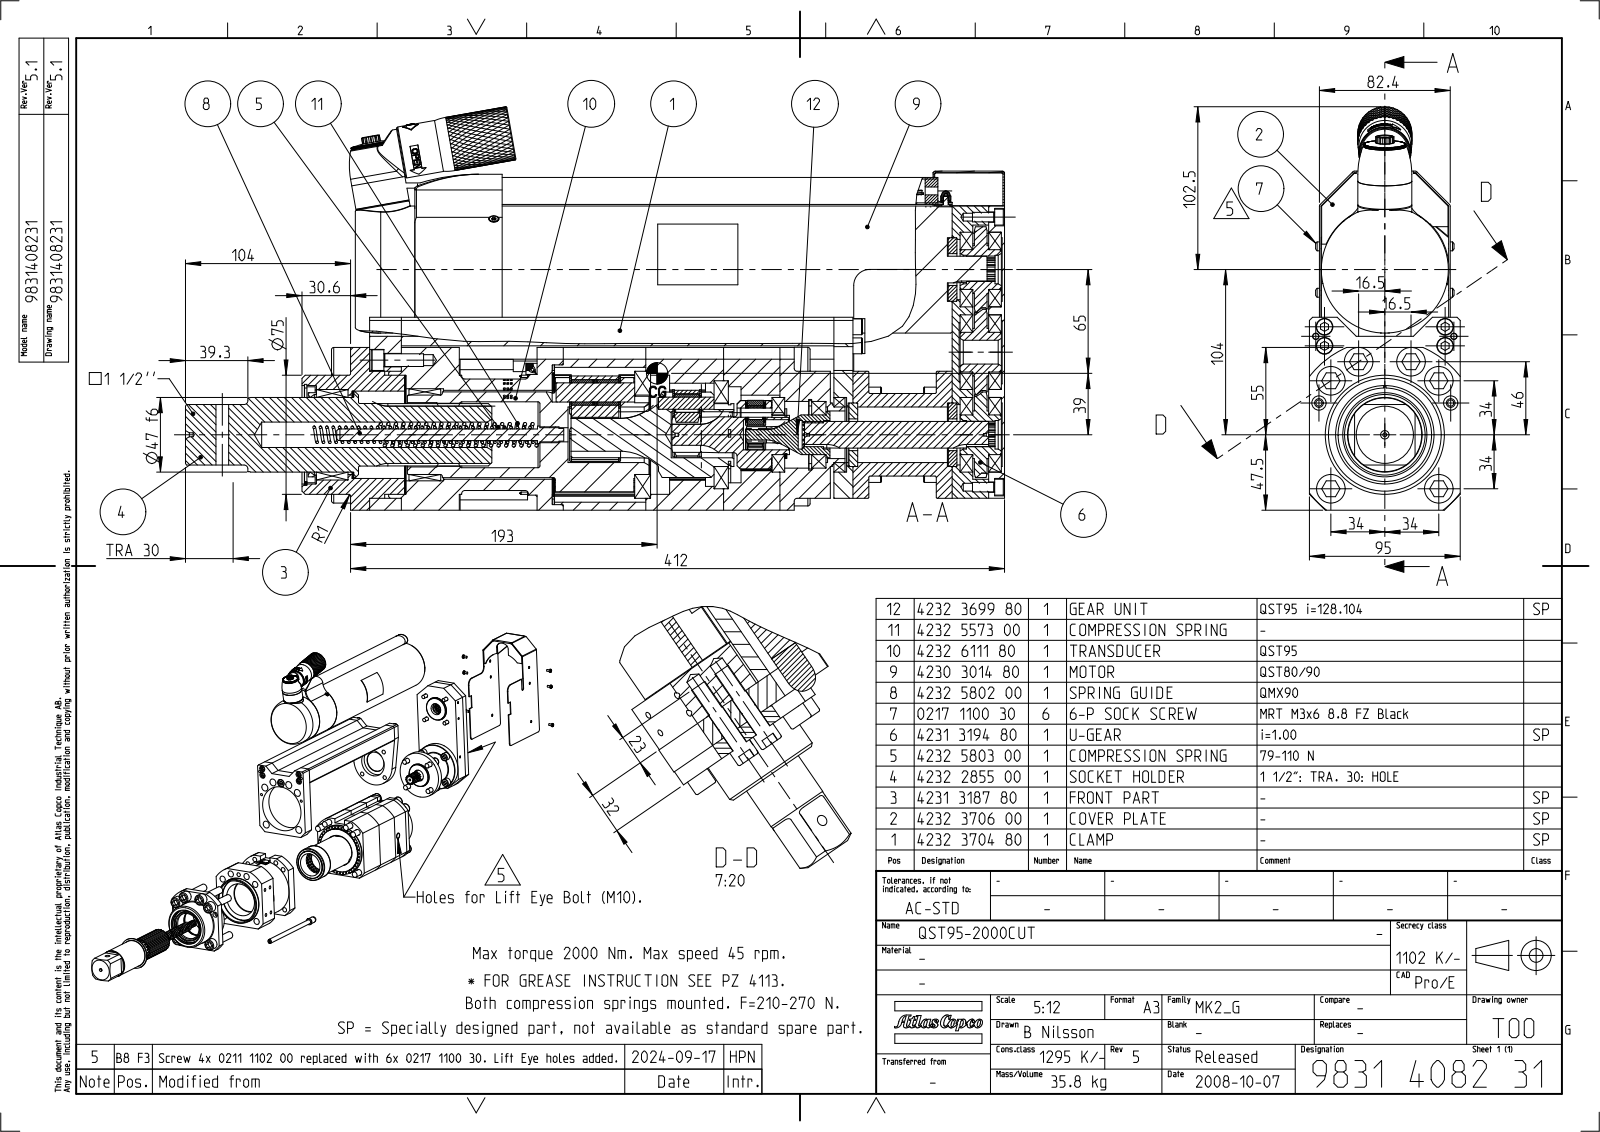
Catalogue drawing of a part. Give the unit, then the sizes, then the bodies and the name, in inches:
Units: inches
Overall size (bounding box): 20.324 × 10.002 × 3.74
Round holes (diameter × count): ⌀0.13 ×8, ⌀0.138 ×6, ⌀0.177 ×6, ⌀0.312 ×6, ⌀0.433 ×6, ⌀0.157 ×4, ⌀0.194 ×4, ⌀0.272 ×4, ⌀0.413 ×4, ⌀0.335 ×3, ⌀0.115 ×2, ⌀0.128 ×2
Round bosses / shafts (diameter × count): ⌀0.394 ×10, ⌀0.709 ×6, ⌀0.63 ×6, ⌀0.118 ×6, ⌀0.512 ×4, ⌀0.236 ×4, ⌀0.22 ×4, ⌀1.339 ×3
Partial cylindrical surfaces — rounded edges, fillets, slot ends (radius × count): R0.011 ×36, R0.02 ×36, R0.02 ×14, R0.059 ×6, R0.094 ×4, R0.128 ×3, R0.031 ×2, R0.077 ×2
Main face-to-face distances: 0.039, 0.287, 3.453, 3.74, 0.248, 3.493, 3.206, 0.472, 4.075, 3.166
Hole centre spacings: 0.74, 1.417, 2.157, 0.472, 2.431, 2.898, 0.32, 1.458
Volume: 369.5 in³ · Surface area: 846.9 in²
Bodies: 12 solids, 2647 faces (1466 planar, 618 cylindrical, 563 other)
Part name (STEP PRODUCT): 9831408231_SW0001
STEP written by: CREO PARAMETRIC BY PTC INC, 2022414 (CONFIG_CONTROL_DESIGN)
